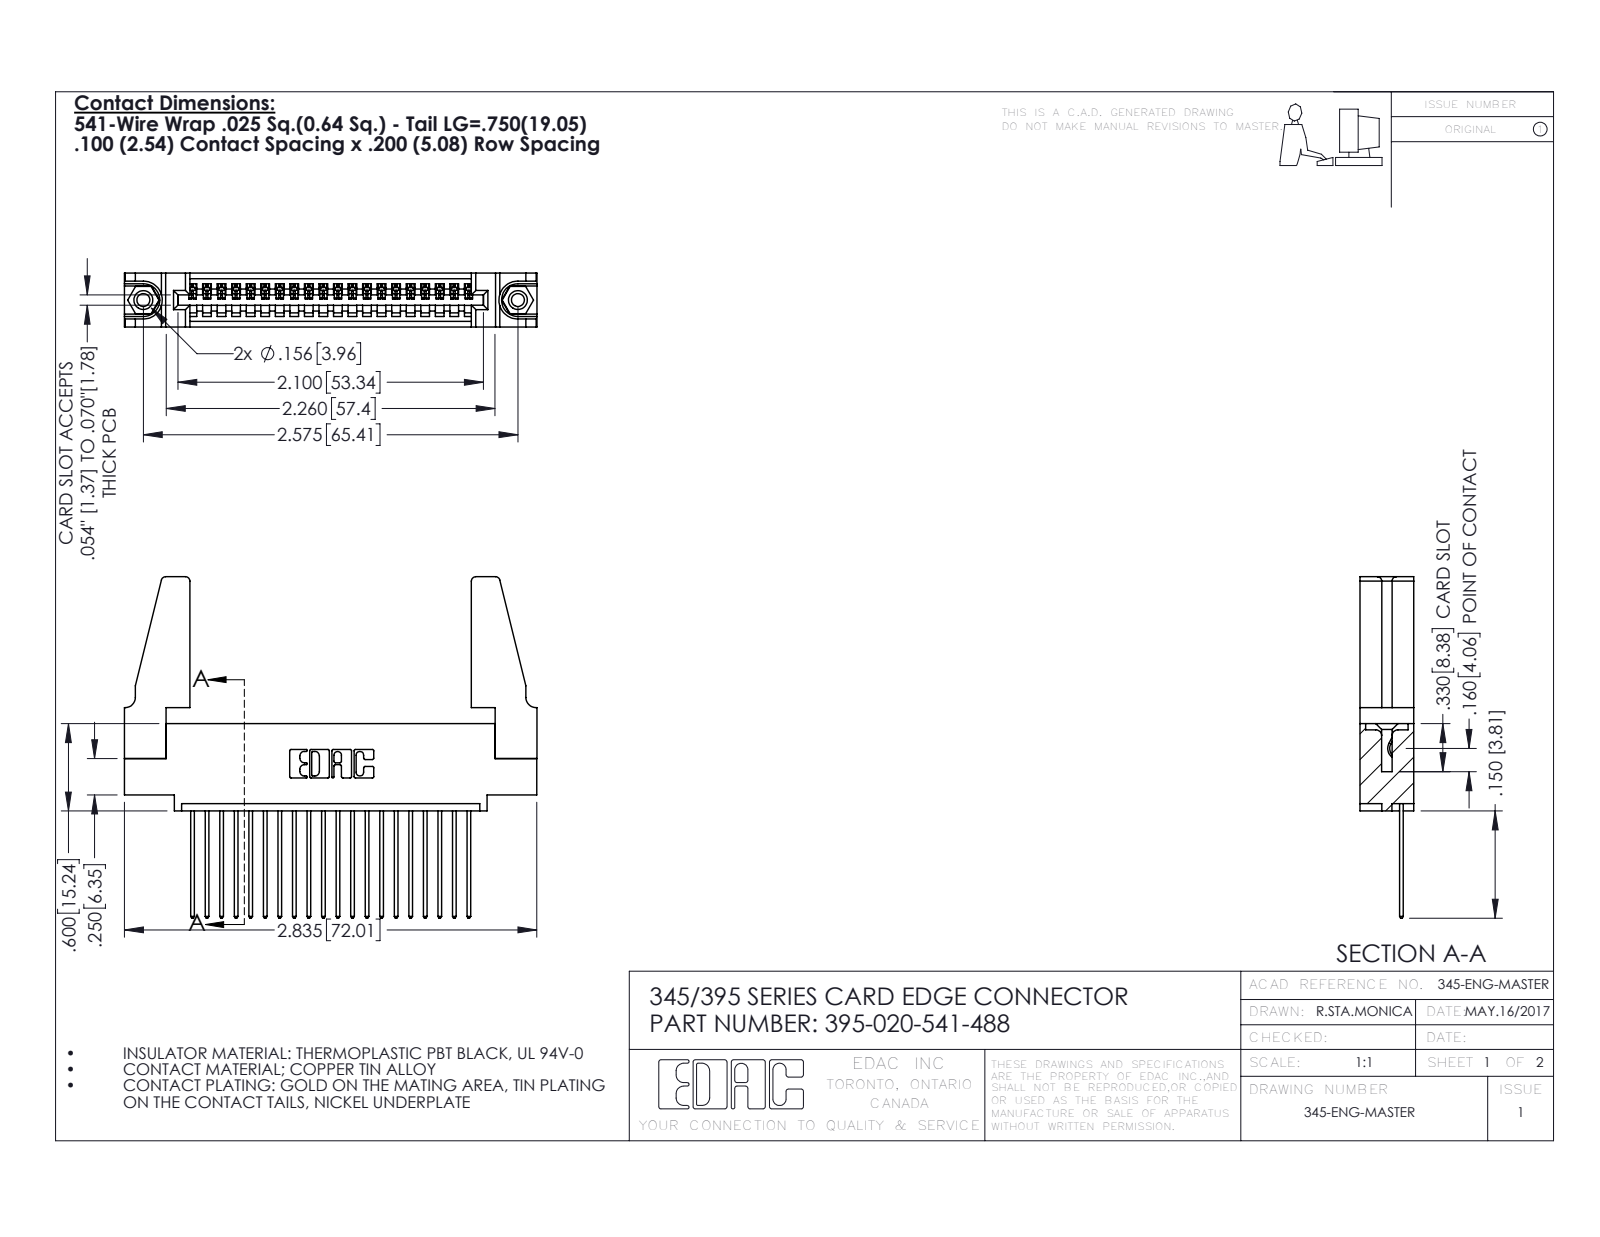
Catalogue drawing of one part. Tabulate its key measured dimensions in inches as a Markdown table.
| quantity | value |
| --- | --- |
| part name | 345-220-078_345-220-088; 345-292-001_345-293-141; 345-250-001_345-250-001-102; 345 Part_0.110 Offset - 0.156 Dia-TH (+1 more) |
| STEP written by | SolidWorks 2016 (CONFIG_CONTROL_DESIGN) |
| units | inches |
| bodies | 25 solids, 1414 faces (956 planar, 442 cylindrical, 16 other) |
| overall size | 2.836 × 2.347 × 0.37 |
| volume | 0.605 in³ |
| surface area | 18.82 in² |
| round holes (diameter × count) | 0.089 × 2, 0.125 × 2, 0.156 × 2, 0.064 × 1 |
| round bosses / shafts (diameter × count) | 0.155 × 2 |
| partial cylindrical surfaces (radius × count) | 0.006 × 40, 0.01 × 40, 0.01 × 22, 0.03 × 8, 0.007 × 6, 0.031 × 6, 0.026 × 3, 0.031 × 2 |
| main face-to-face distances | 0.072, 0.37, 0.298, 0.098, 0.272, 0.025, 0.2, 0.225, 0.148, 0.15 |
| hole center spacings | 0.27, 2.341, 2.575 |
